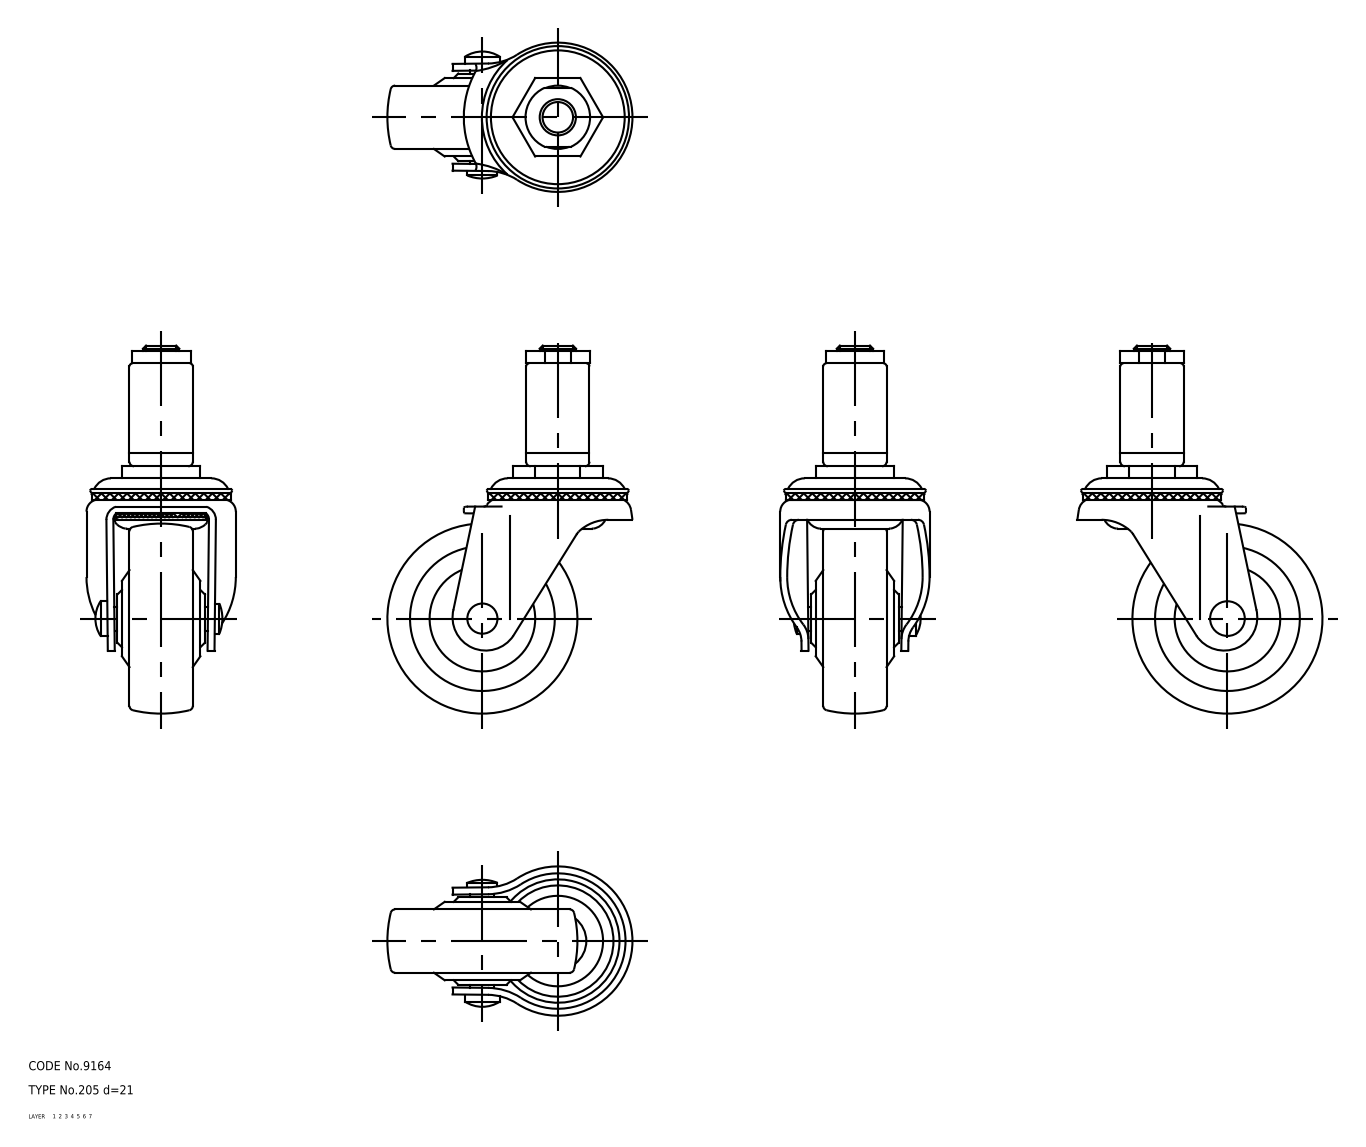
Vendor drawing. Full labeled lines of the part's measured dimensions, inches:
Part name (STEP PRODUCT): wheel; main shaft; axle; No_205_d21_21549_36
STEP written by: CADfix (AUTOMOTIVE_DESIGN)
Units: inches
Bodies: 4 solids, 206 faces (0 planar, 0 cylindrical, 206 other)
Overall size (bounding box): 4.803 × 3.199 × 1.949
Volume: 6.499 in³ · Surface area: 47.9 in²
